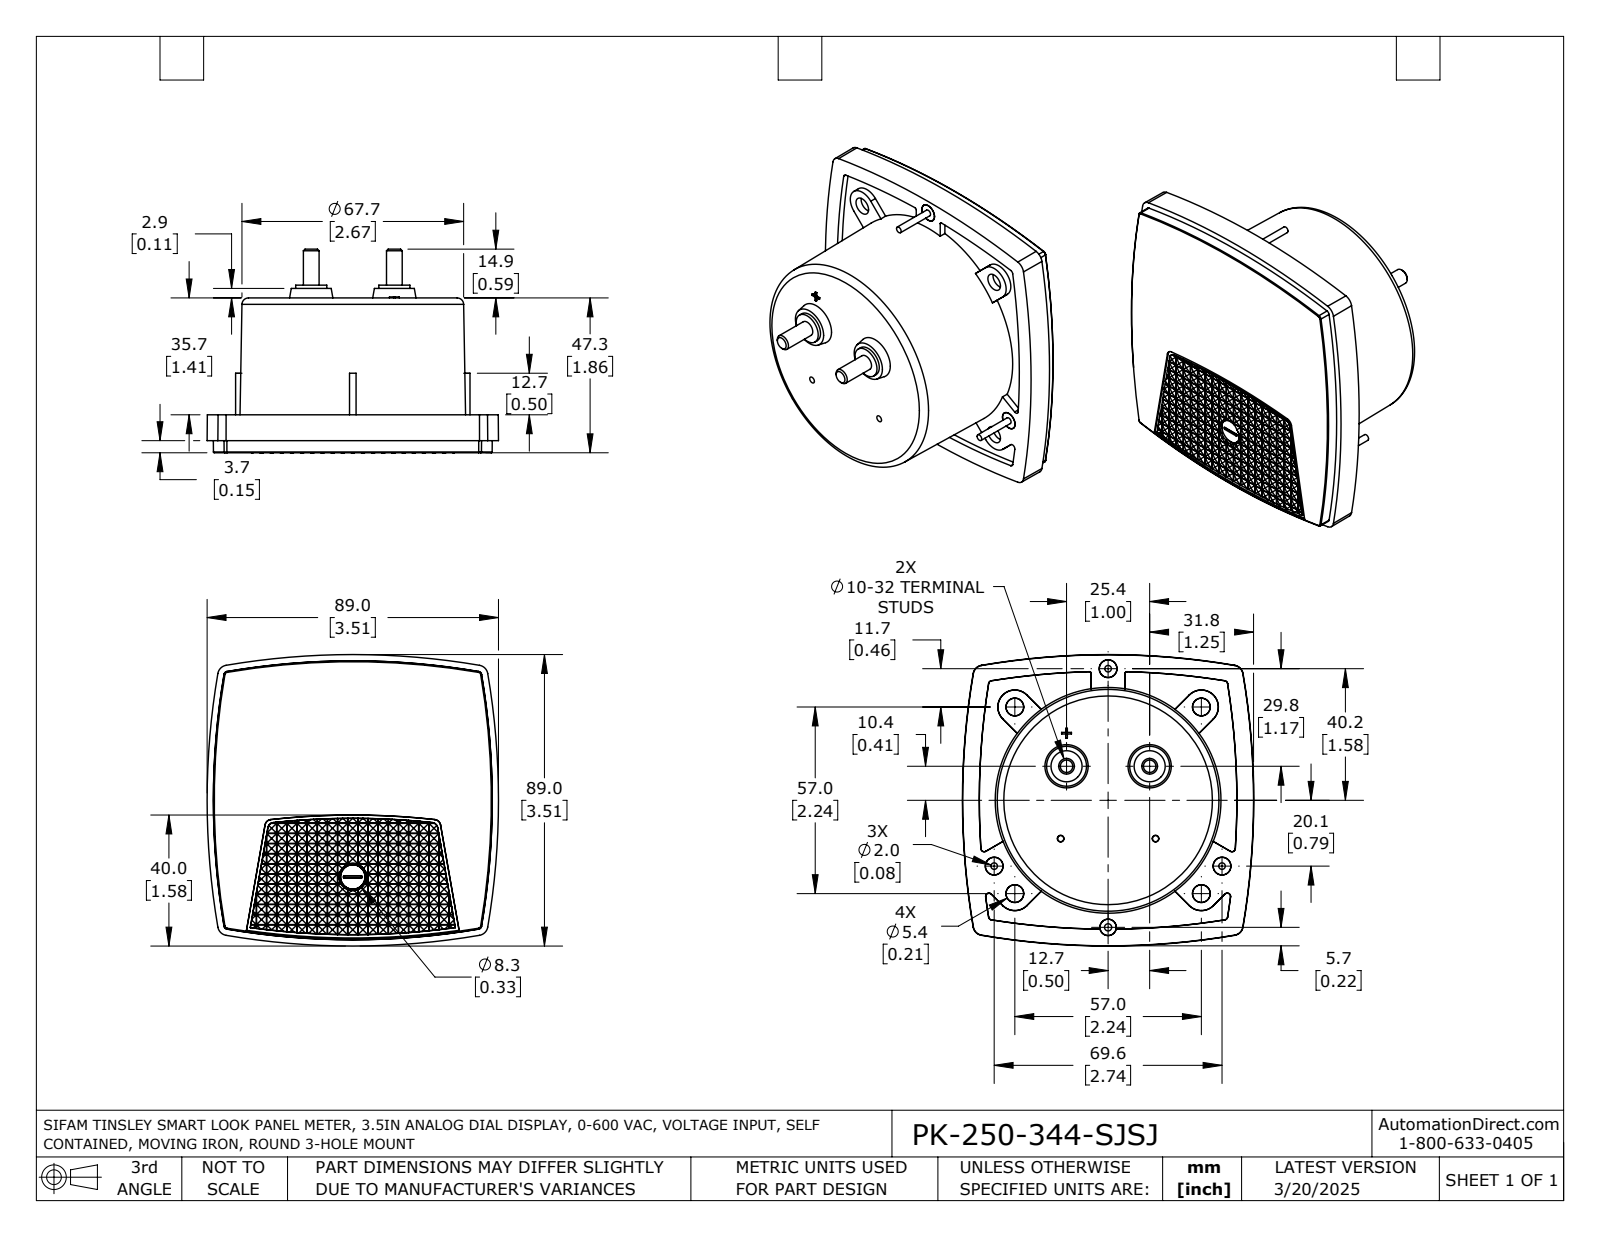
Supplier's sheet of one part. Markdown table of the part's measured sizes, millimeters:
| quantity | value |
| --- | --- |
| part name | PK-250-344-SJSJ |
| STEP written by | SolidWorks 2021 (AUTOMOTIVE_DESIGN) |
| units | millimeters |
| bodies | 1 solid, 1078 faces (950 planar, 23 cylindrical, 105 other) |
| overall size | 89 × 89 × 62.3 |
| volume | 212 900 mm³ |
| surface area | 28 570 mm² |
| round holes (diameter × count) | 2.2 × 1 |
| round bosses / shafts (diameter × count) | 5.4 × 3, 2 × 3, 9.5 × 2, 4.8 × 2 |
| partial cylindrical surfaces (radius × count) | 227.6 × 1 |
| main face-to-face distances | 47.3, 35.7, 11.6, 2, 37.7, 9.6, 0.6, 2.4, 1.8, 3 |
